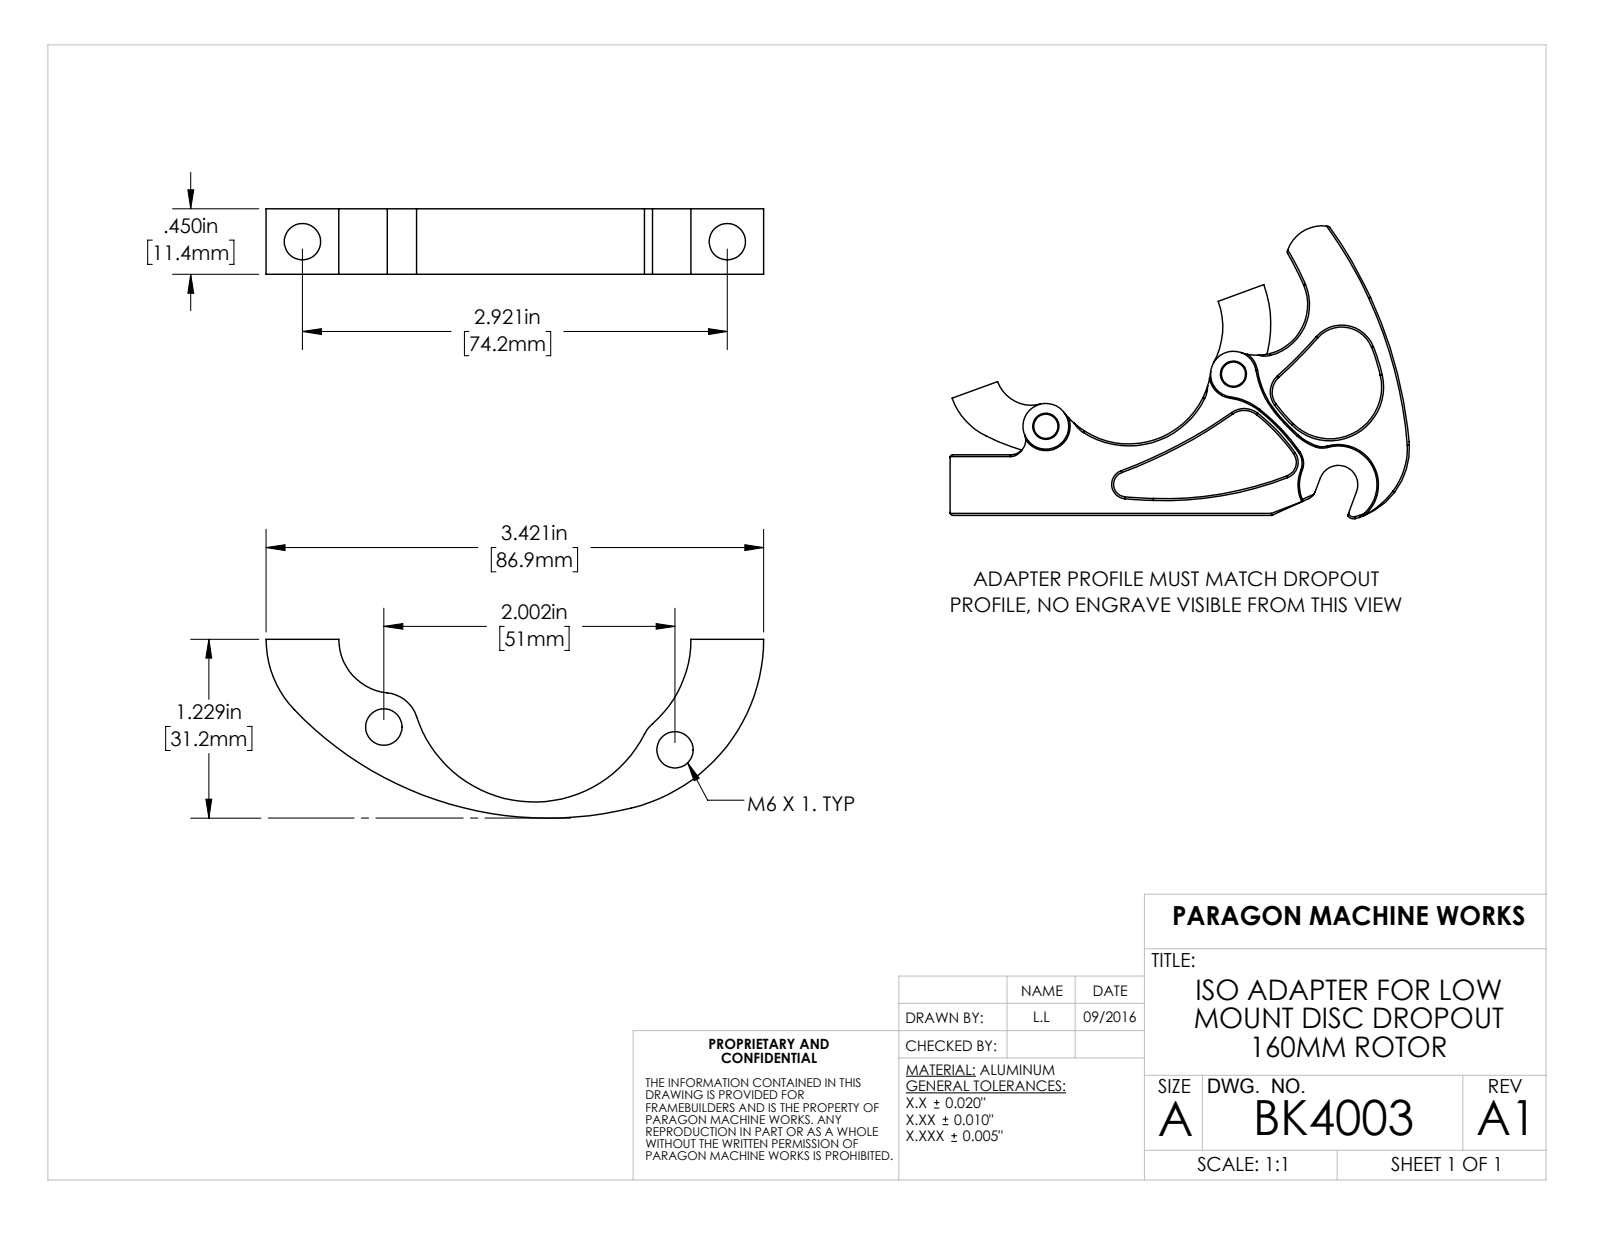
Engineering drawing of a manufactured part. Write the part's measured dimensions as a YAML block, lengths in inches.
part_name: "BK4003"
step_written_by: "SolidWorks 2018 (AUTOMOTIVE_DESIGN)"
units: inches
bodies: {solids: 1, faces: 20, planar: 4, cylindrical: 16, other: 0}
overall_size: [3.421, 1.229, 0.45]
volume: 0.541
surface_area: 8.27
round_holes:
  - {diameter: 0.25, count: 4}
partial_cylinders:
  - {radius: 0.236, count: 2}
  - {radius: 0.37, count: 1}
  - {radius: 0.7, count: 1}
  - {radius: 0.771, count: 1}
  - {radius: 0.85, count: 1}
  - {radius: 1.194, count: 1}
  - {radius: 2.412, count: 1}
face_to_face_distances: [0.45]
hole_center_spacings: [2.008, 2.921]
